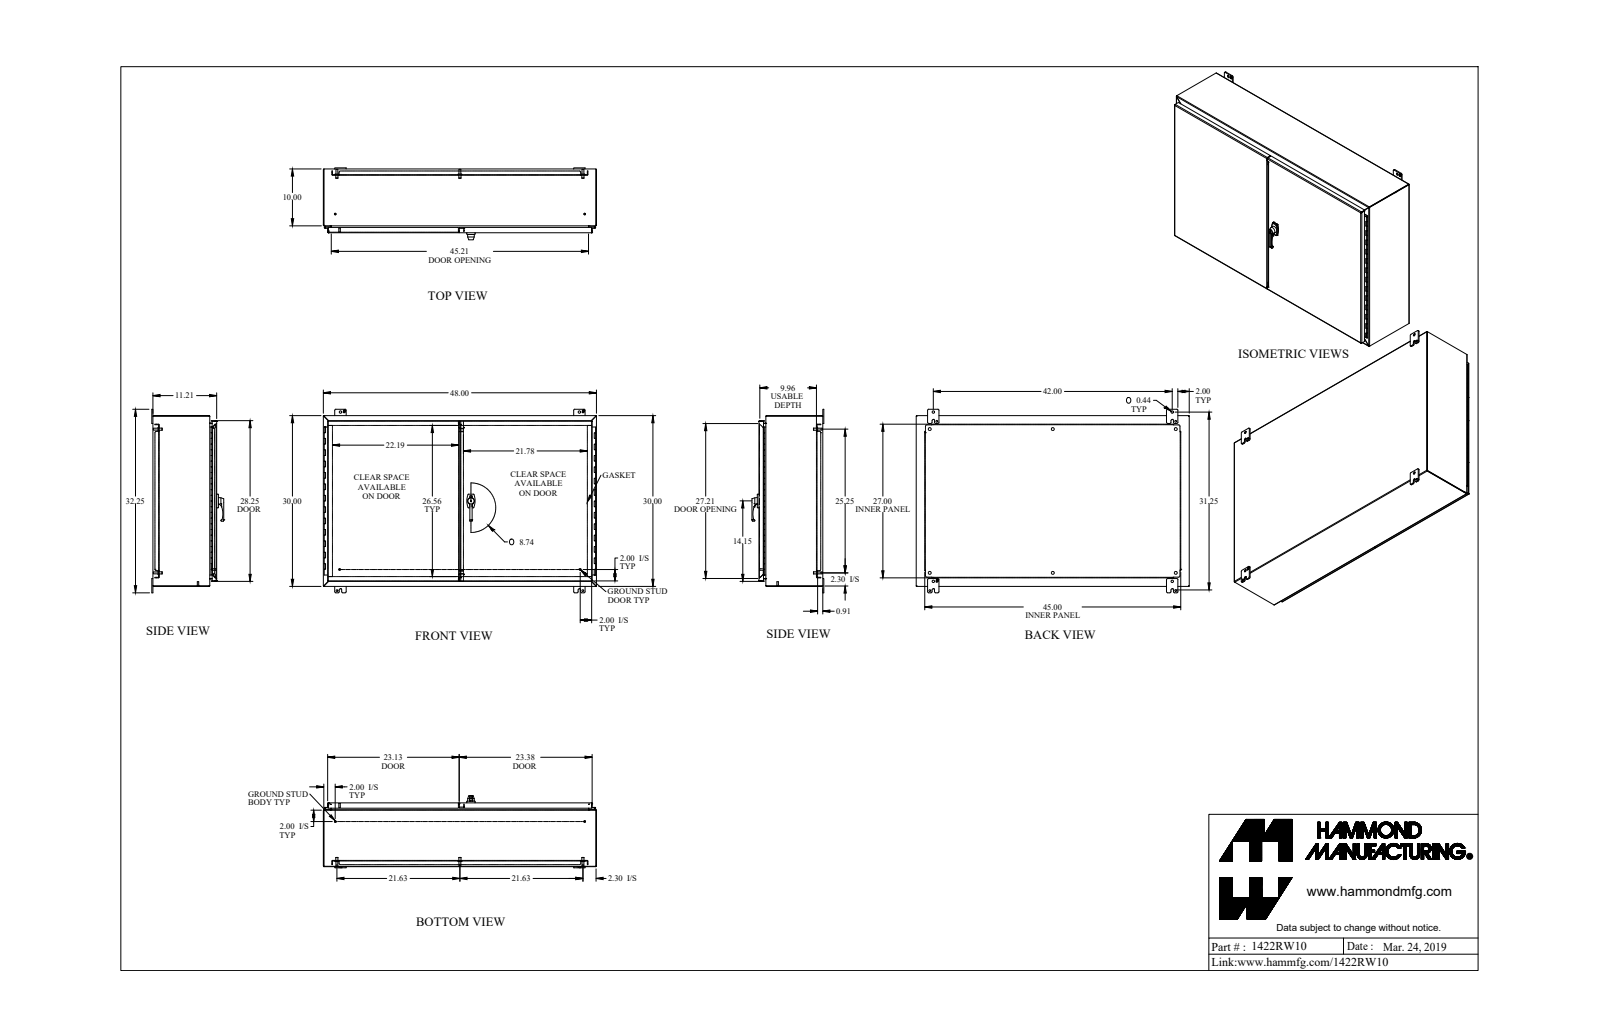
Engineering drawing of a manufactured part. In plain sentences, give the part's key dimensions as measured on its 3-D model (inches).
The part is named "1422RW10". Its 3-D file was written by "SolidWorks 2019 (AUTOMOTIVE_DESIGN)". It is 0 solids with 1669 faces: 1024 planar, 495 cylindrical and 150 other. Overall it measures 48 by 32.25 by 12.637 inches. Round holes: 10 of diameter 0.304, 7 of diameter 0.307, 6 of diameter 0.5, 4 of diameter 0.218, 4 of diameter 0.313, 4 of diameter 0.437, 4 of diameter 0.445, 3 of diameter 0.215, 2 of diameter 0.11, 2 of diameter 0.127, 2 of diameter 0.156, 2 of diameter 0.187. Round bosses or shafts: 7 of diameter 1, 6 of diameter 0.65, 6 of diameter 0.375, 6 of diameter 0.33, 5 of diameter 0.5, 4 of diameter 0.313, 4 of diameter 0.281, 4 of diameter 0.25. Partial cylindrical surfaces (rounded edges, fillets, slot ends): 36 of radius 0.188, 18 of radius 0.048, 18 of radius 0.143, 16 of radius 0.036, 16 of radius 0.05, 16 of radius 0.108, 13 of radius 0.25, 12 of radius 0.116. The main face-to-face distances are 0.072, 11.043, 11.115, 0.095, 0.095, 0.937, 11.138, 11.21, 10.106, 10.011. The hole center spacings are 21.625, 6, 46.778, 1.691, 12, 23.204, 24.124, 29.748.
